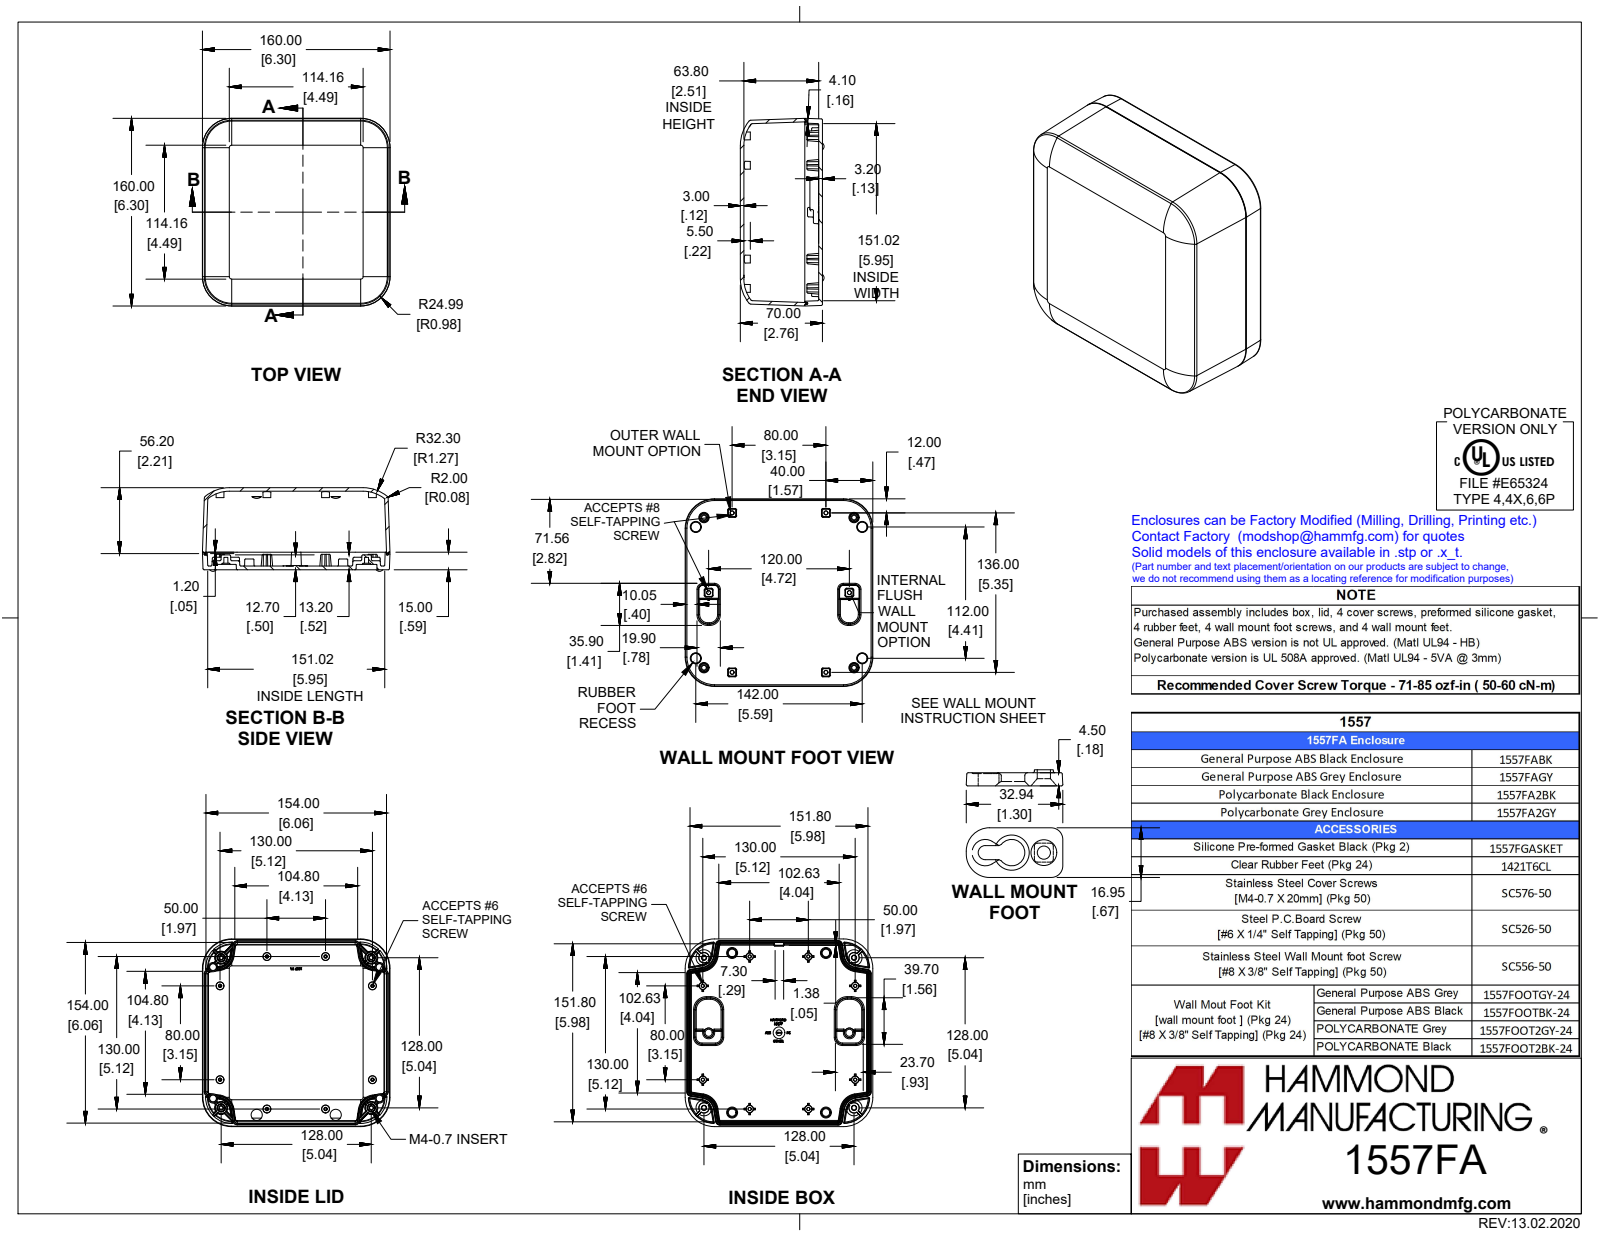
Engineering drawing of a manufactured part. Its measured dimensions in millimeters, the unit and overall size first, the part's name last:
Units: millimetres
Overall size (bounding box): 189 × 160 × 74.5
Round holes (diameter × count): ⌀3.3 ×4, ⌀4.5 ×4
Round bosses / shafts (diameter × count): ⌀1.8 ×12, ⌀8 ×4, ⌀7.7 ×4, ⌀6.4 ×4, ⌀5.5 ×4, ⌀5.3 ×4, ⌀4.2 ×4, ⌀3.9 ×4
Partial cylindrical surfaces — rounded edges, fillets, slot ends (radius × count): R0.5 ×101, R1 ×78, R4 ×12, R0.2 ×8, R0.3 ×8, R0.4 ×8, R1.5 ×8, R2.1 ×8
Main face-to-face distances: 3, 3.2, 67, 63.8, 70, 66.8, 156.8, 159.8, 3, 4.1
Hole centre spacings: 24.3, 104.1, 128, 134.2, 168, 80, 136, 157.8
Volume: 320 000 mm³ · Surface area: 225 900 mm²
Bodies: 23 solids, 2924 faces (974 planar, 573 cylindrical, 1377 other)
Part name (STEP PRODUCT): 1557FA TOP; 1557F gasket; IN-M4 (insert M4-0.7X5.75mm SS) KNURLS; (screw #8X 3_8''''''''FH Self-tap plastite) (+5 more)
STEP written by: SolidWorks 2019 (CONFIG_CONTROL_DESIGN)
